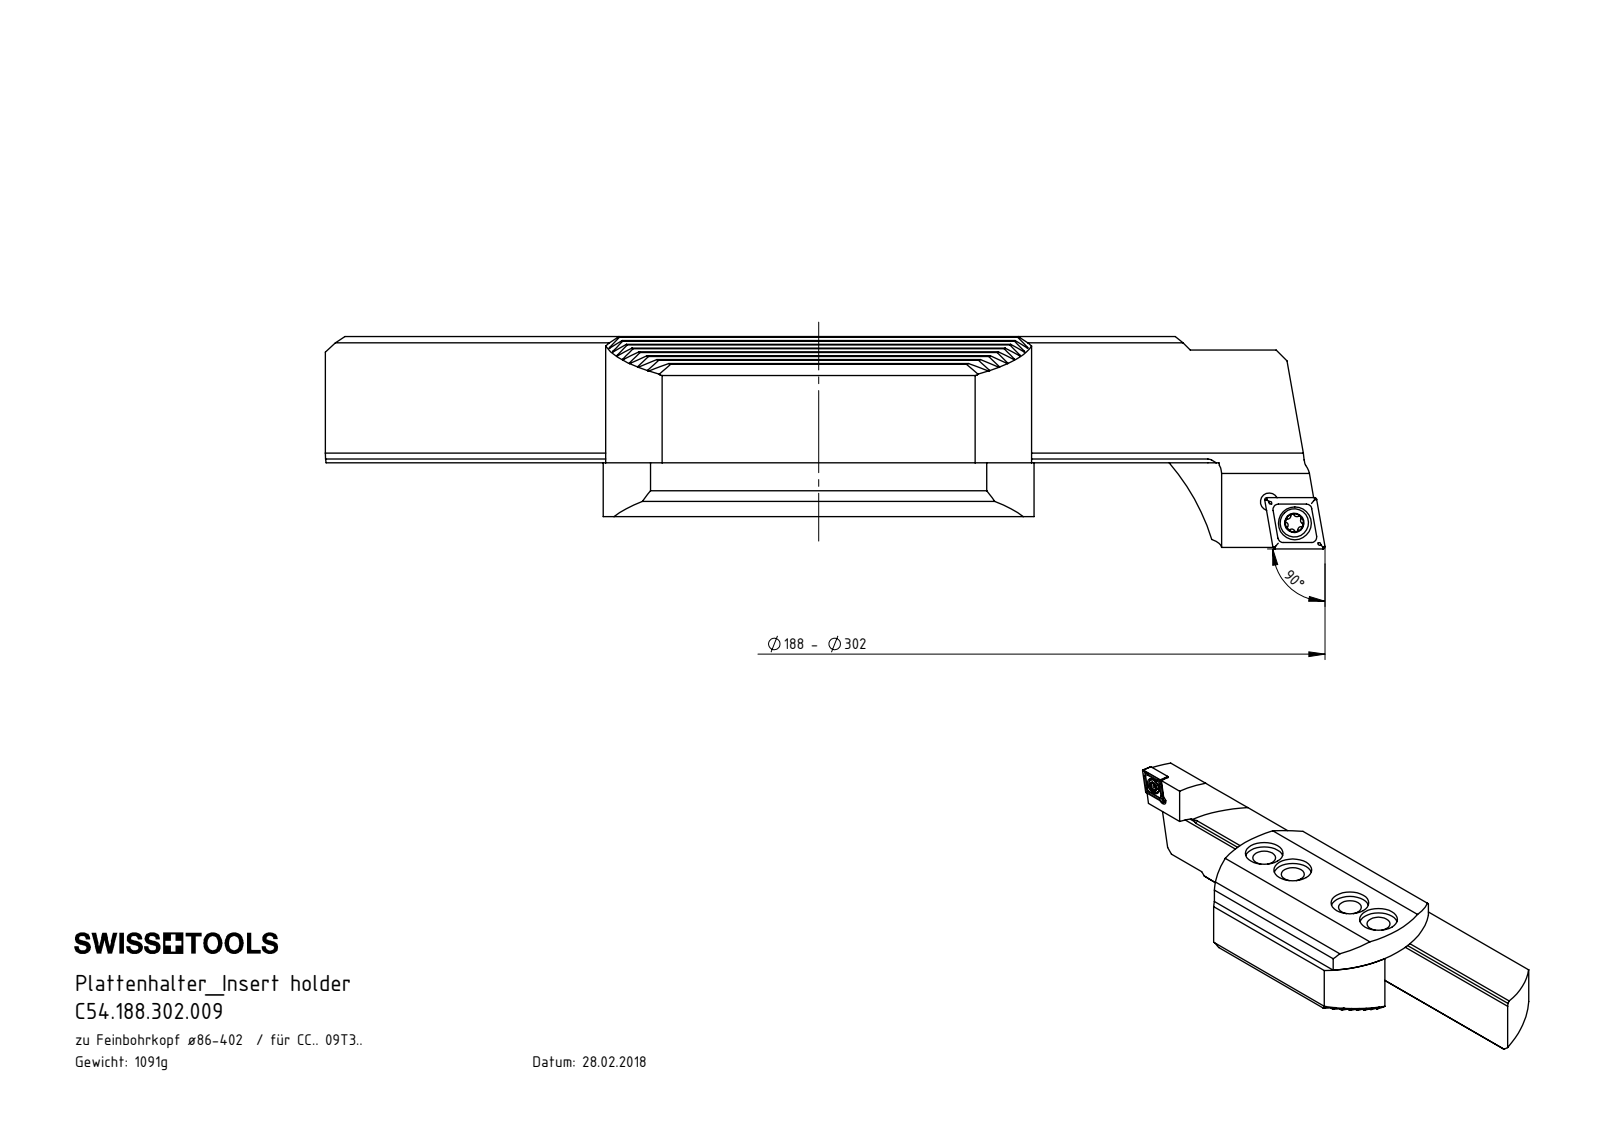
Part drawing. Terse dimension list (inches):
name: F00-WCB.188.001_C; WCB-ER2.001.009_A; CCMT09T304; F00-WCB.188.001_mit Wp (+3 more)
written by: SolidWorks 2017 (CONFIG_CONTROL_DESIGN)
unit: in
bodies: 5 solids, 770 faces (462 planar, 67 cylindrical, 241 other)
size: 7.306 × 2.165 × 1.551
volume: 8.482 in³; area: 56.9 in²
holes: 4× ⌀0.335, 4× ⌀0.551, 2× ⌀0.13, 1× ⌀0.173, 1× ⌀0.24
bosses: 1× ⌀0.207, 1× ⌀0.157
rounds: 16× R0.008, 6× R0.013, 6× R0.023, 6× R1.575, 1× R0.031
face distances: 0.094, 0.187, 0.839, 1.327, 0.281, 0.375, 0.488, 0.188, 0.281, 0.375
hole spacings: 0.591, 1.772, 0.239, 0.244, 1.181, 2.362
